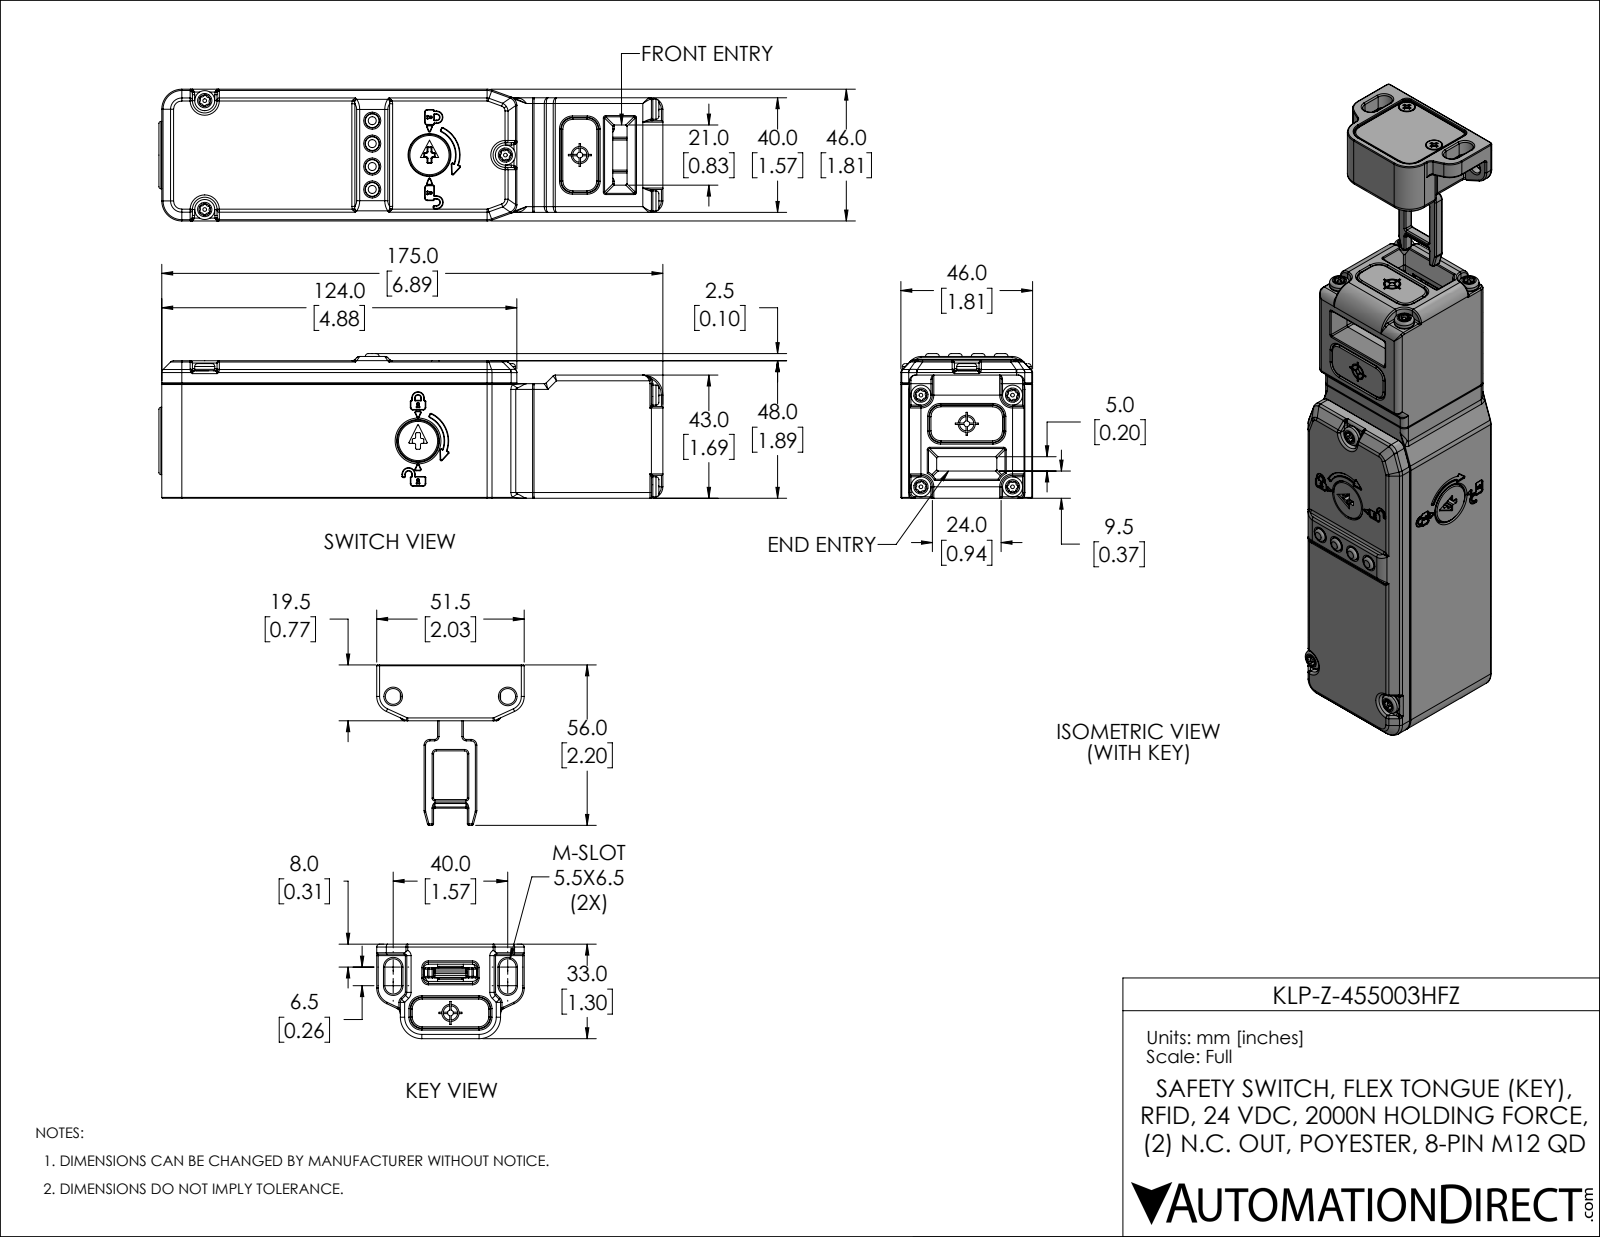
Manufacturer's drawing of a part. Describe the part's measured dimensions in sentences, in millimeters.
The part is named "455-KLP-Z-HFZ". Its 3-D file was written by "SolidWorks 2019 (AUTOMOTIVE_DESIGN)". It is 26 solids with 4195 faces: 1222 planar, 1686 cylindrical and 1287 other. Overall it measures 237 by 51.5 by 50.5 millimeters. Its volume is 299 600 cubic millimeters and its surface area 95 810 square millimeters. Round holes: 13 of diameter 4, 6 of diameter 2.4, 6 of diameter 5, 6 of diameter 6, 4 of diameter 4.5, 4 of diameter 9.3, 3 of diameter 3.5, 3 of diameter 3.6, 3 of diameter 4.3, 3 of diameter 5.5, 2 of diameter 2.5, 2 of diameter 3.3. Round bosses or shafts: 11 of diameter 3.5, 7 of diameter 7, 7 of diameter 1.3, 6 of diameter 4.8, 5 of diameter 5, 4 of diameter 5.5, 4 of diameter 2.8, 4 of diameter 1. Partial cylindrical surfaces (rounded edges, fillets, slot ends): 552 of radius 0.5, 188 of radius 0.3, 134 of radius 1, 124 of radius 0.2, 58 of radius 2, 35 of radius 1.5, 33 of radius 4, 16 of radius 0.4. The main face-to-face distances are 40, 3, 46, 43, 8, 1, 48, 2, 2.5, 36.8. The hole center spacings are 8, 8.1, 12.2, 16, 19, 22.6, 26.5, 26.5.
